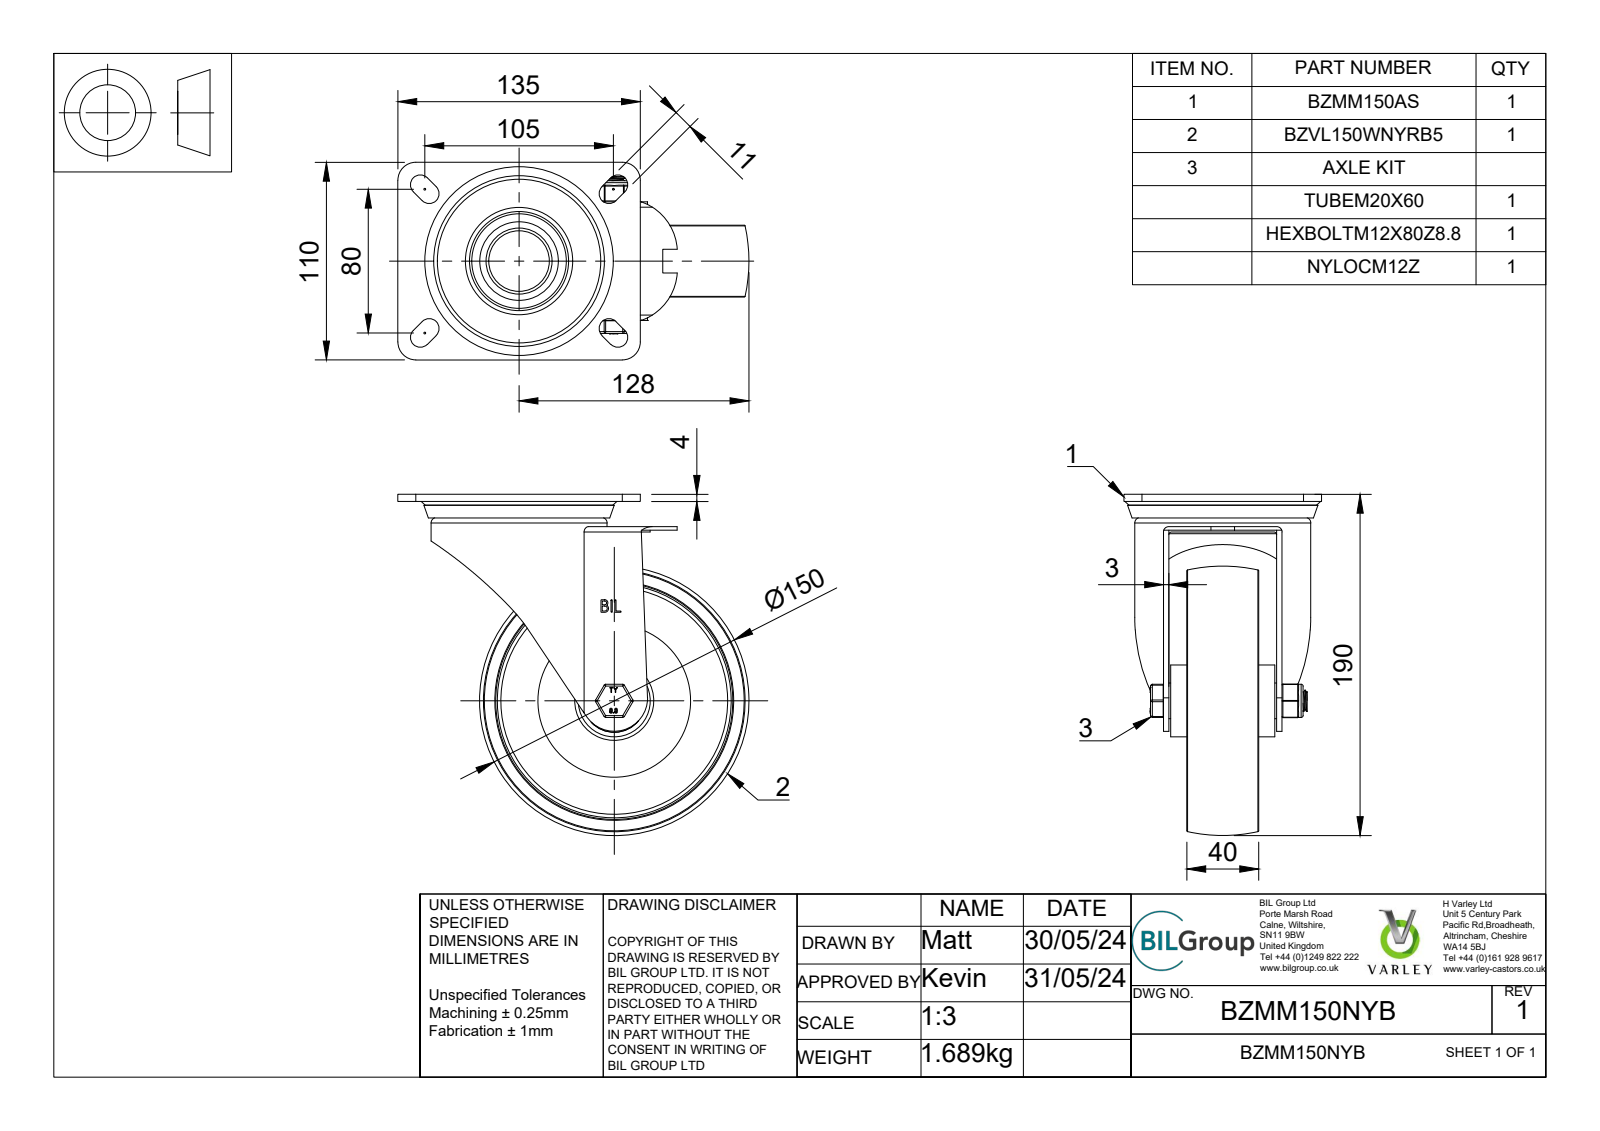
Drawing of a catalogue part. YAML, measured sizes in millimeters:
part_name: "BZMM150NYB v4; BZMM150AS - 2 v3; ZINC PLATED, PRESSED STEEL TOP PLATE; ZINC PLATED, PRESSED STEEL TOP PLATE Geometry (+7 more)"
step_written_by: "Autodesk Translation Framework v13.14.0.145 (AUTOMOTIVE_DESIGN)"
units: millimeters
bodies: {solids: 58, faces: 485, planar: 196, cylindrical: 146, other: 143}
overall_size: [195.5, 190, 110]
volume: 502600
surface_area: 215089
round_holes:
  - {diameter: 12, count: 1}
  - {diameter: 12.2, count: 1}
  - {diameter: 12.5, count: 1}
  - {diameter: 14, count: 1}
  - {diameter: 20, count: 1}
  - {diameter: 20.2, count: 1}
  - {diameter: 33.75, count: 1}
  - {diameter: 35, count: 1}
  - {diameter: 39.75, count: 1}
  - {diameter: 92, count: 1}
round_bosses_or_shafts:
  - {diameter: 7.5, count: 8}
  - {diameter: 98, count: 1}
  - {diameter: 78, count: 1}
  - {diameter: 50, count: 1}
  - {diameter: 40, count: 1}
  - {diameter: 34, count: 1}
  - {diameter: 19.9, count: 1}
  - {diameter: 18.5, count: 1}
partial_cylinders:
  - {radius: 0.5, count: 18}
  - {radius: 1, count: 12}
  - {radius: 5.5, count: 8}
  - {radius: 1.5, count: 4}
  - {radius: 10, count: 4}
  - {radius: 3, count: 2}
  - {radius: 29.97, count: 2}
  - {radius: 13.5, count: 1}
face_to_face_distances: [9, 4, 5, 3, 16, 13, 8, 29, 26, 34]
